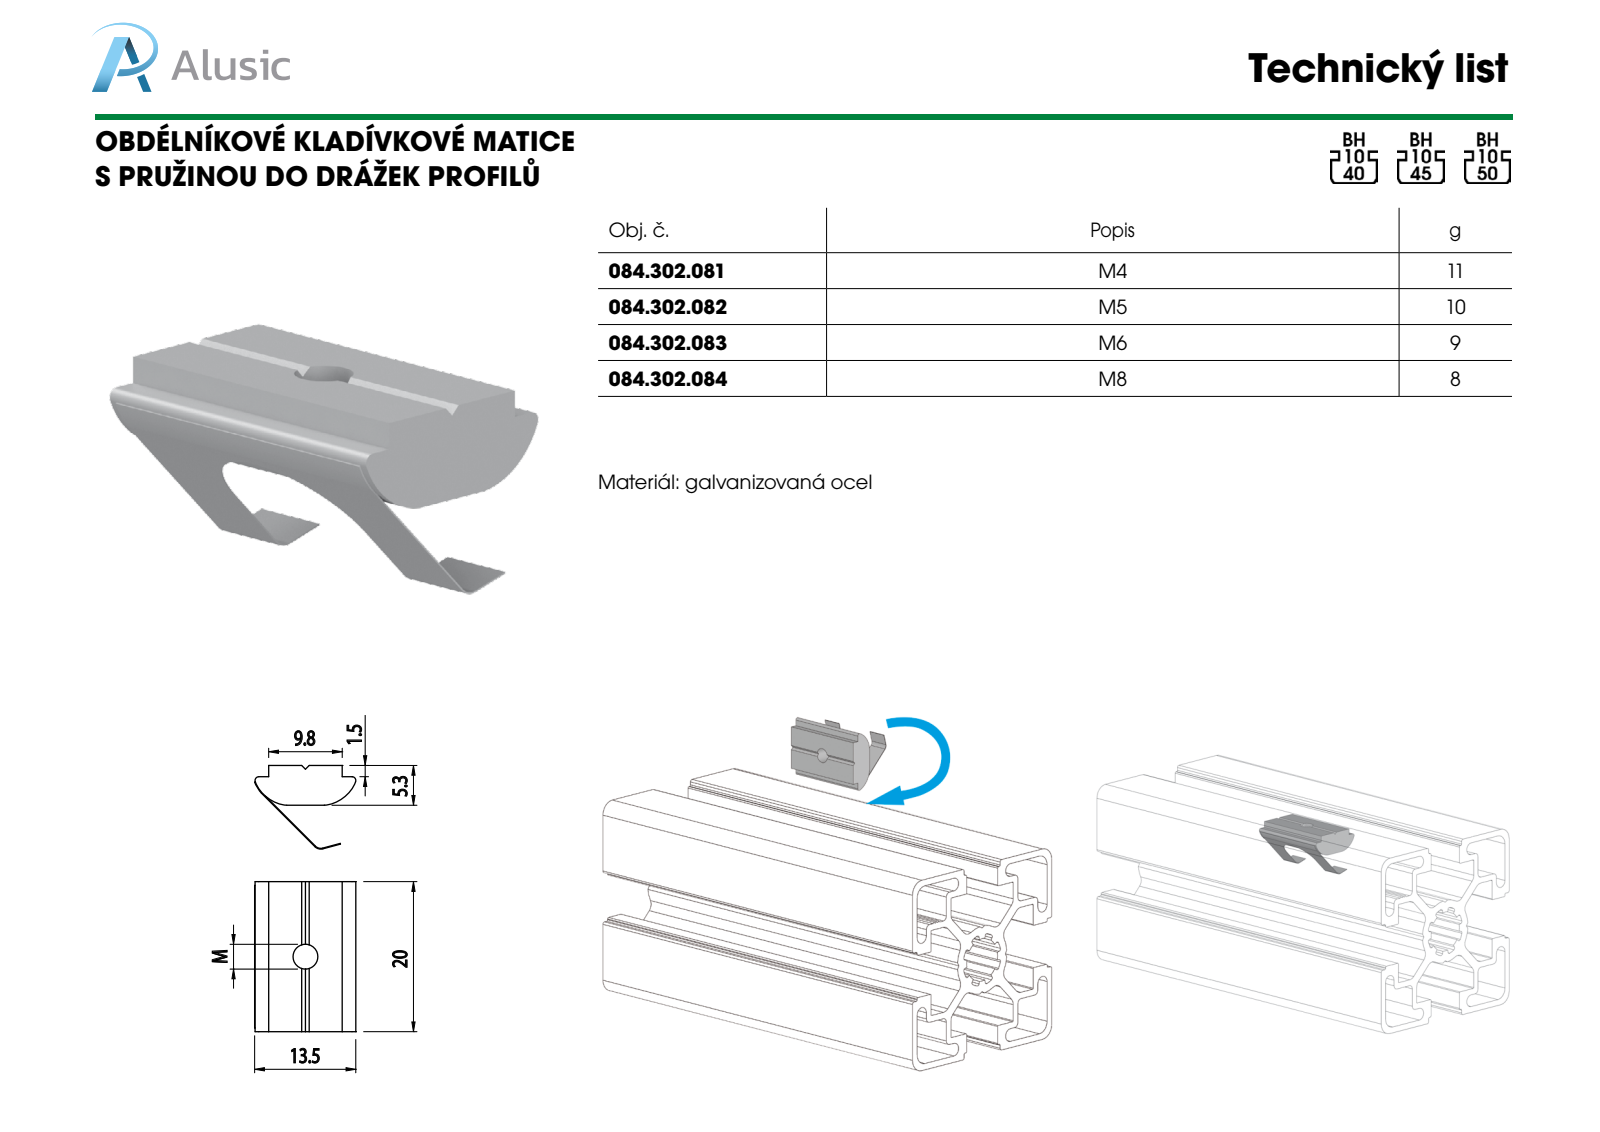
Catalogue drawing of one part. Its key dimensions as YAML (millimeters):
part_name: "084.302.082"
step_written_by: "SolidWorks 2012 (CONFIG_CONTROL_DESIGN)"
units: millimeters
bodies: {solids: 1, faces: 45, planar: 32, cylindrical: 13, other: 0}
overall_size: [20, 13.49, 11.15]
volume: 1091
surface_area: 1095
round_holes:
  - {diameter: 4.2, count: 1}
partial_cylinders:
  - {radius: 5, count: 3}
  - {radius: 0.5, count: 2}
  - {radius: 1, count: 1}
  - {radius: 1.1, count: 1}
  - {radius: 5.1, count: 1}
face_to_face_distances: [5.3, 20, 3.8, 1.5, 9.8, 6.41, 6.31, 0.5, 19.5, 5]
